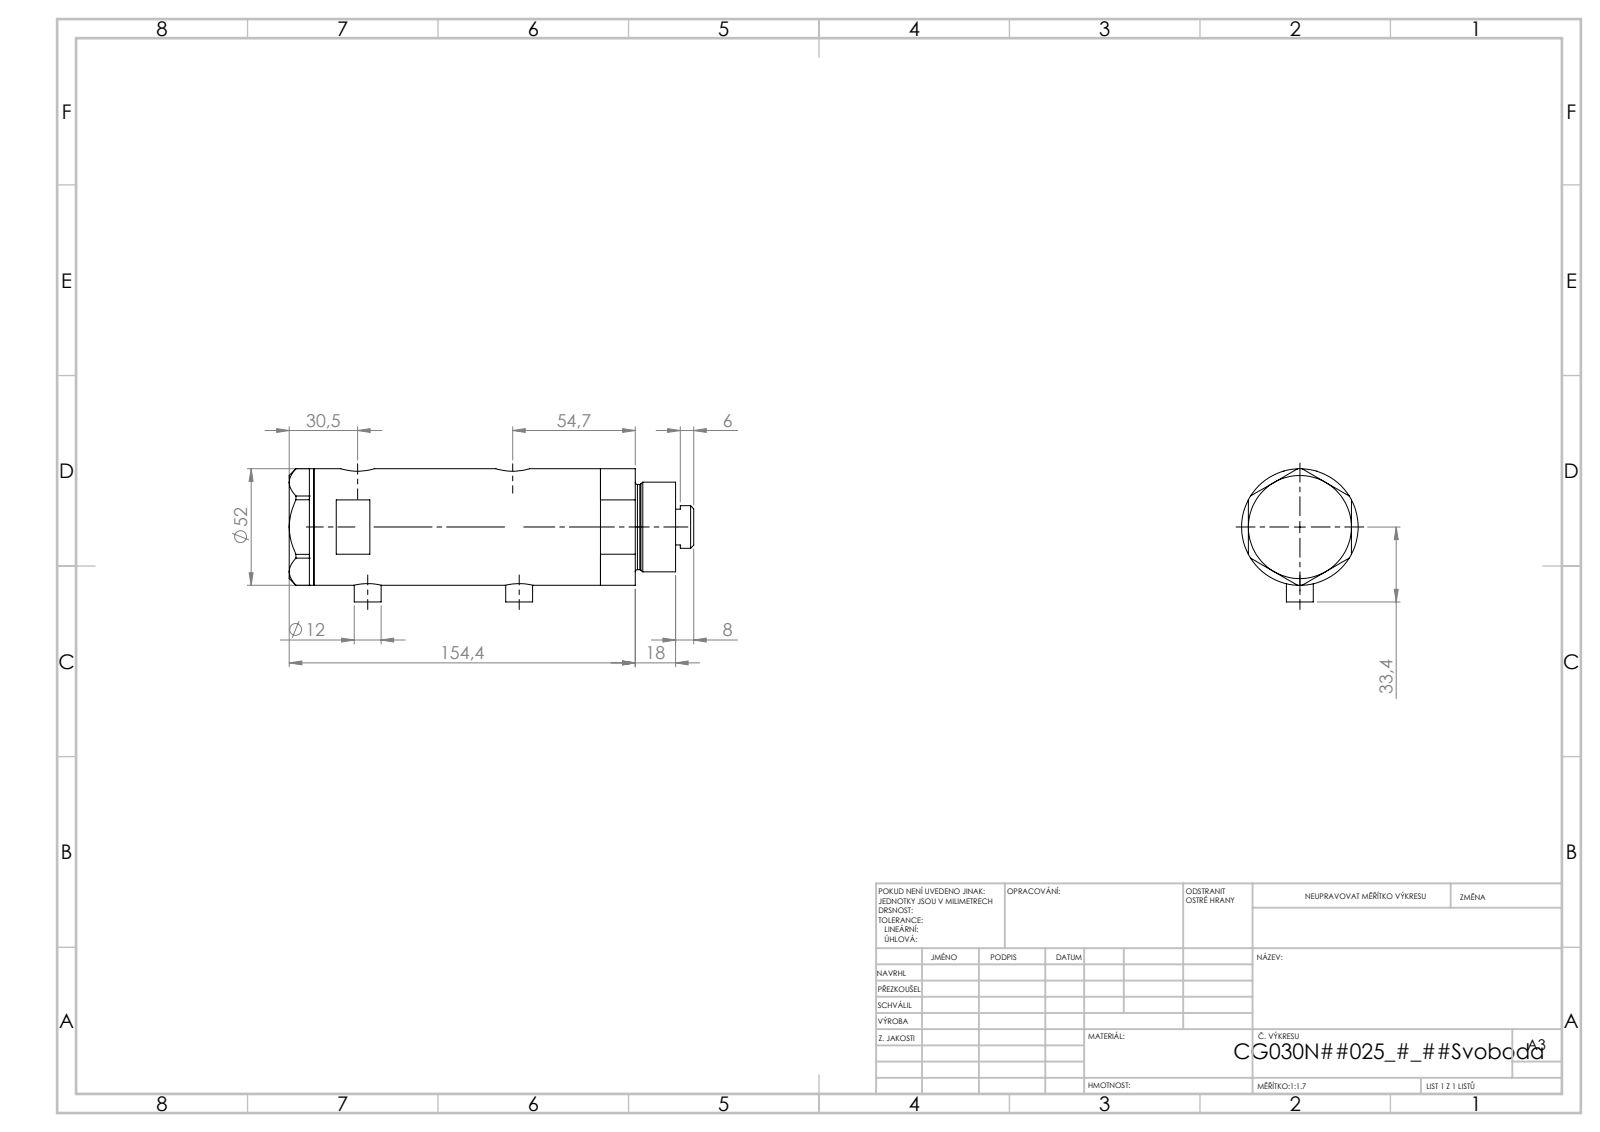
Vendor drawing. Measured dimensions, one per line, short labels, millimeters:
name: V270CG_MIDDLE; V270CG_FRONT; V270CG_BACK; V270CG_VC
written by: SolidWorks 2019 (CONFIG_CONTROL_DESIGN)
unit: mm
bodies: 4 solids, 140 faces (67 planar, 53 cylindrical, 20 other)
size: 180.5 × 59.4 × 52
volume: 331 897 mm³; area: 77 189 mm²
holes: 2× ⌀5, 2× ⌀9.73, 2× ⌀12.5, 2× ⌀15, 1× ⌀6.5, 1× ⌀20, 1× ⌀21.5, 1× ⌀30, 1× ⌀33, 1× ⌀44
bosses: 2× ⌀12, 1× ⌀52, 1× ⌀40, 1× ⌀38, 1× ⌀19
face distances: 91.5, 23.8, 67.7, 11, 34.8, 102.5, 46, 138.9, 127.9, 104.1
hole spacings: 2.9, 4.5, 64.7, 67.6, 69.2, 72.1
